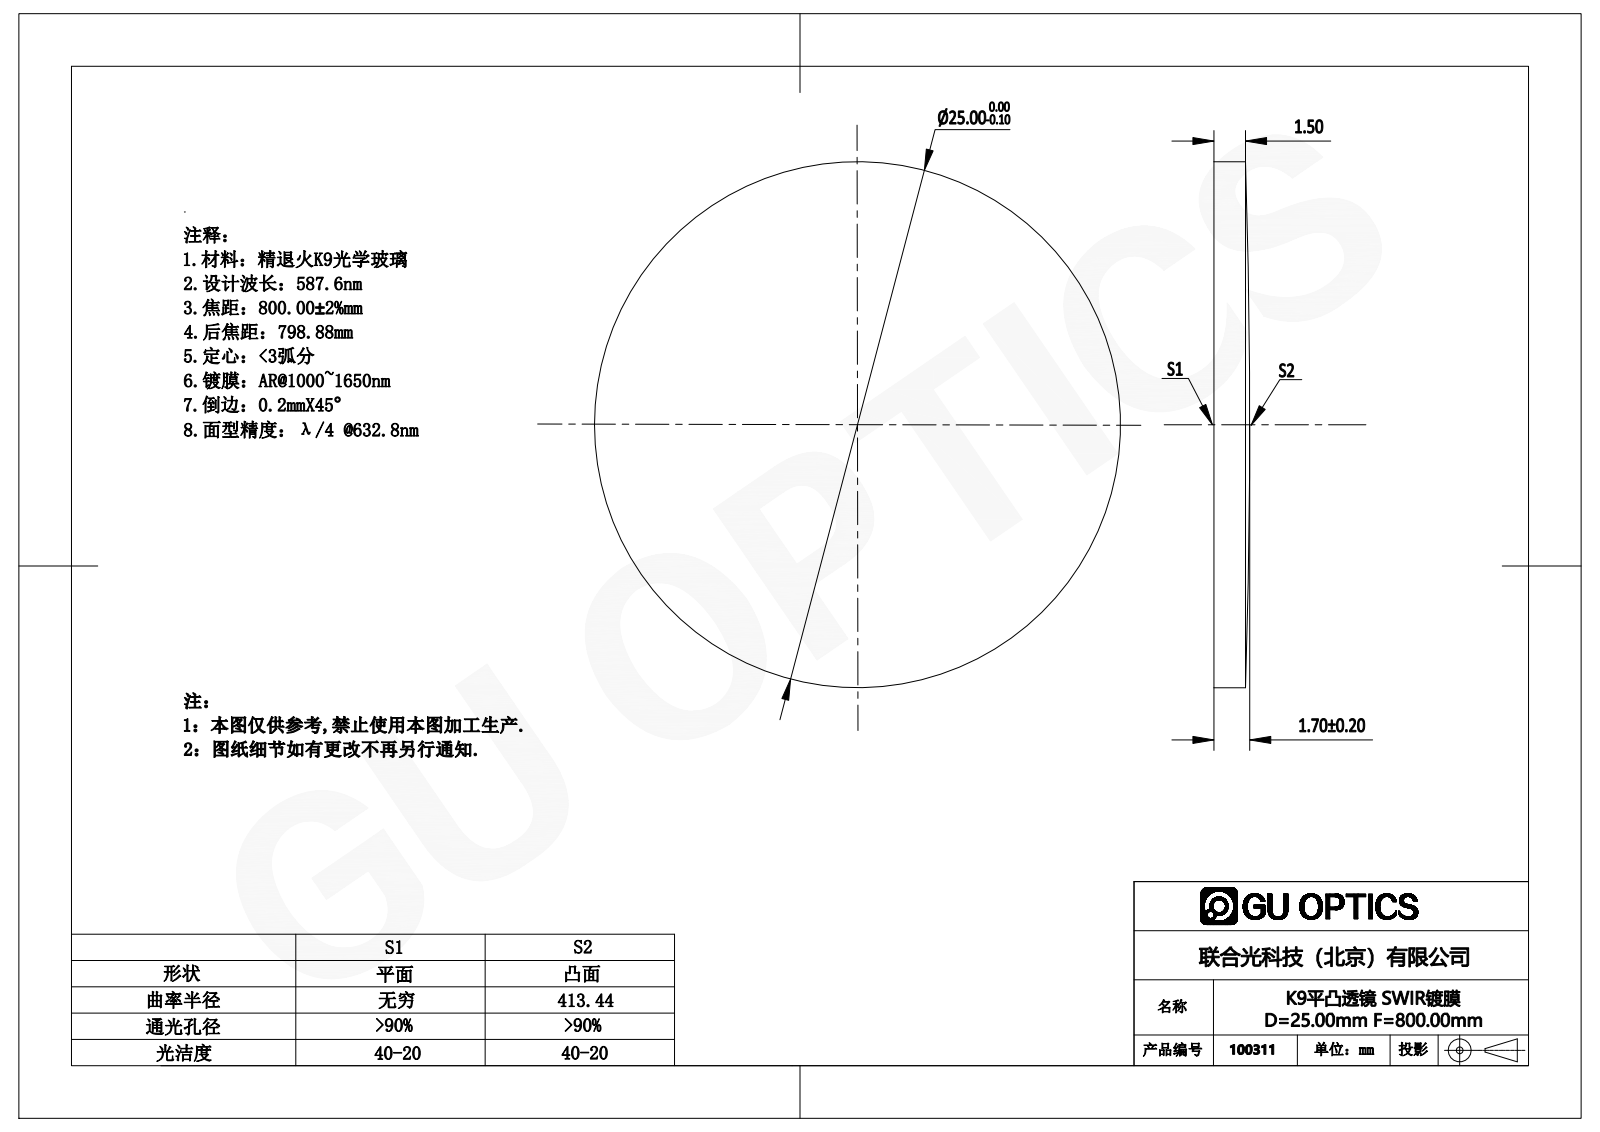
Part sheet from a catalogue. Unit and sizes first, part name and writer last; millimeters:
Units: millimetres
Overall size (bounding box): 25 × 25 × 1.7
Round bosses / shafts (diameter × count): ⌀25 ×1
Volume: 785 mm³ · Surface area: 1 100 mm²
Bodies: 1 solid, 5 faces (1 planar, 2 cylindrical, 2 other)
Part name (STEP PRODUCT): 100139
STEP written by: SolidWorks 2016 (AUTOMOTIVE_DESIGN)
